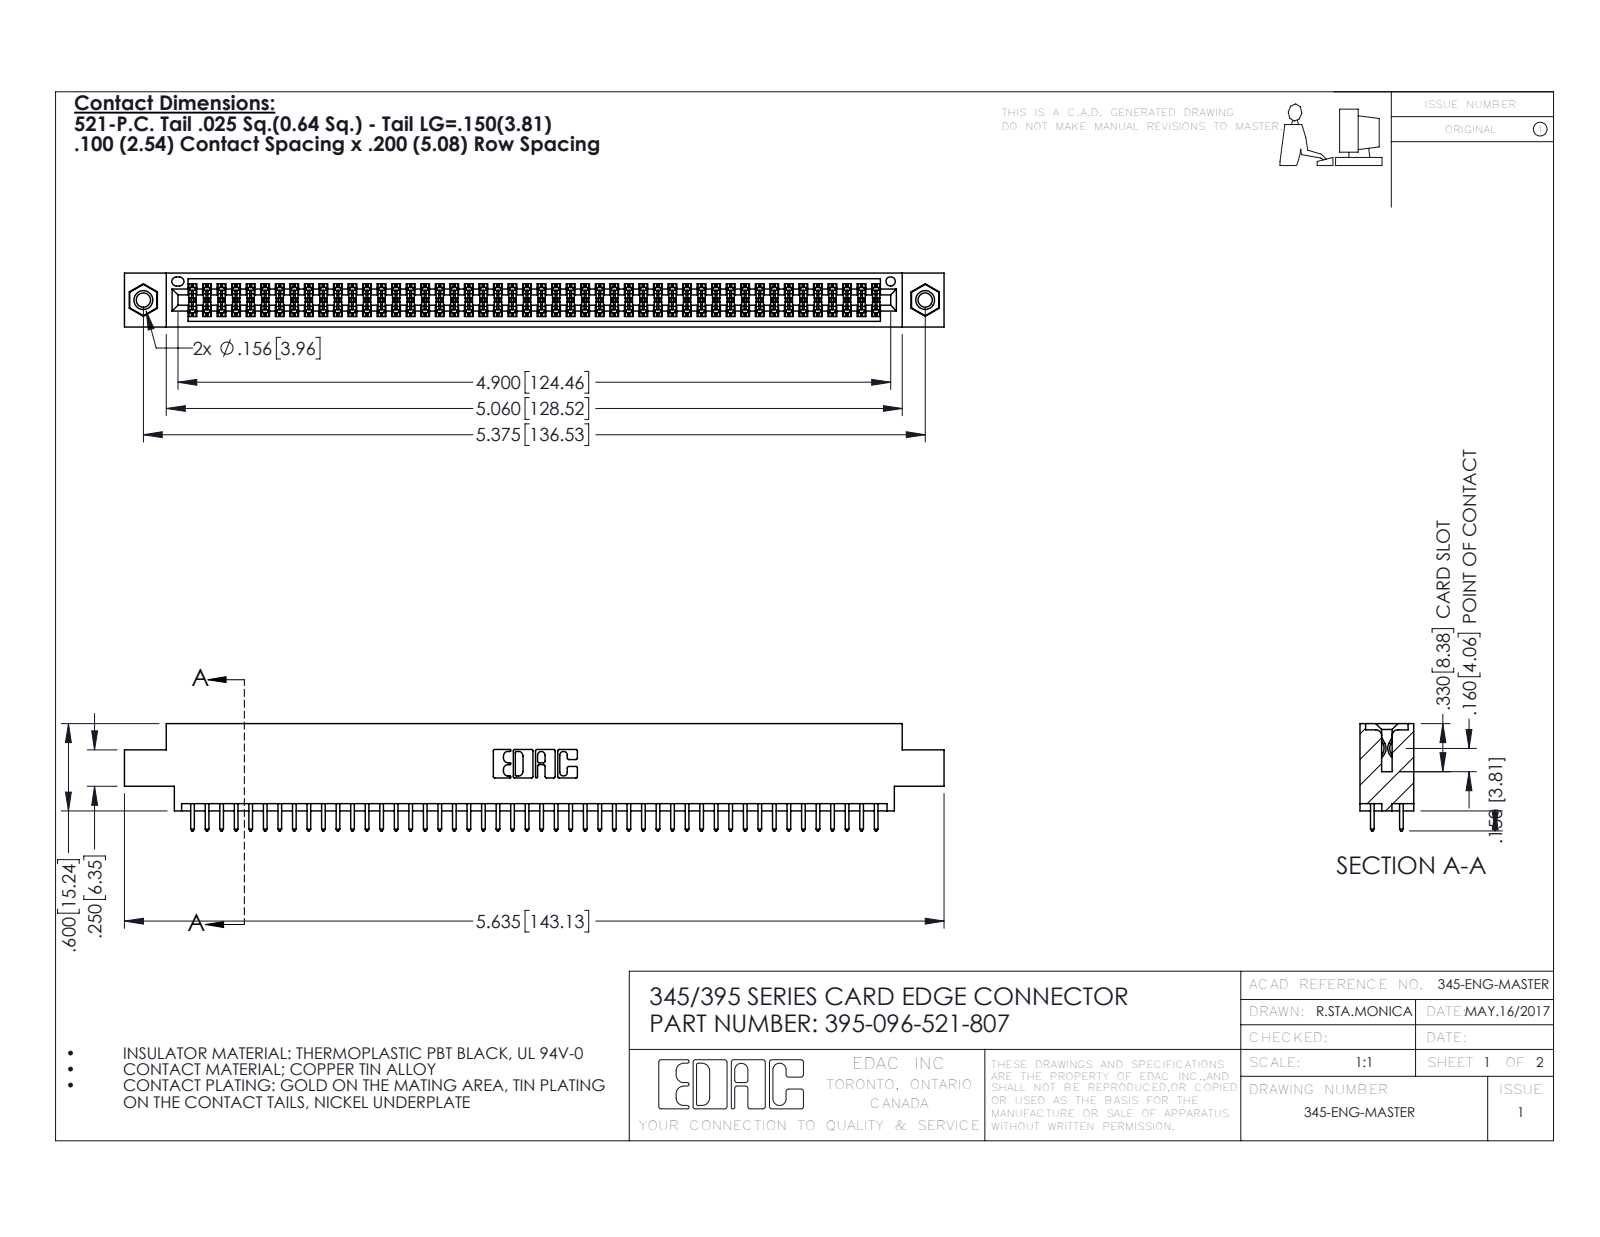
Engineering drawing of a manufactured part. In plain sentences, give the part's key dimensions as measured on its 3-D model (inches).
The part is named "345-292-001_345-293-121; 395-096-521-807; 345-250-001_345-250-005-103; 345 Part_0.170 Offset - 0.156 Dia-TI". Its 3-D file was written by "SolidWorks 2016 (CONFIG_CONTROL_DESIGN)". It is 99 solids with 4990 faces: 3284 planar, 1690 cylindrical and 16 other. Overall it measures 5.635 by 0.737 by 0.37 inches. Its volume is 0.842 cubic inches and its surface area 31.65 square inches. Round holes: 2 of diameter 0.098, 2 of diameter 0.125, 2 of diameter 0.156, 1 of diameter 0.064. Round bosses or shafts: 2 of diameter 0.155. Partial cylindrical surfaces (rounded edges, fillets, slot ends): 144 of radius 0.006, 96 of radius 0.01, 22 of radius 0.01, 6 of radius 0.007, 6 of radius 0.031, 3 of radius 0.026, 2 of radius 0.014, 2 of radius 0.019. The main face-to-face distances are 0.072, 0.298, 0.2, 0.37, 0.098, 0.272, 0.025, 0.225, 0.175, 0.149. The hole center spacings are 0.27, 5.139, 5.375.
